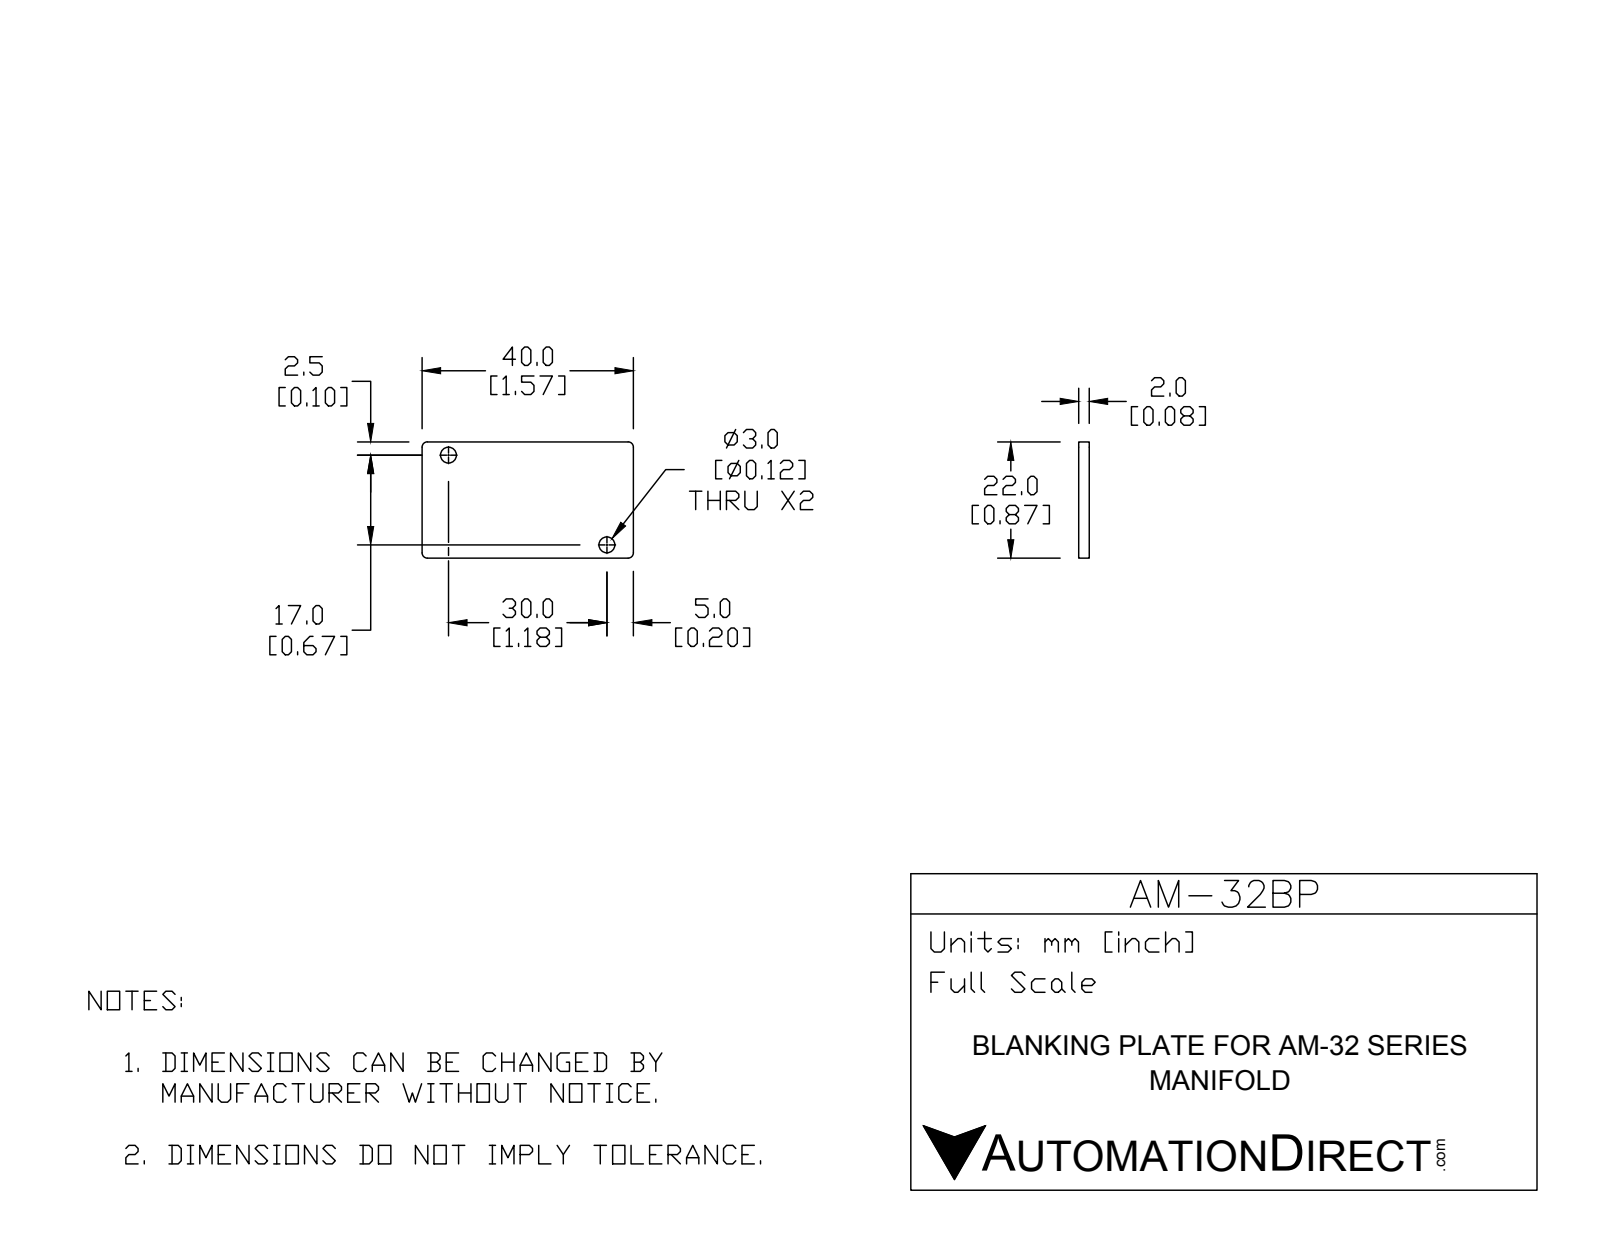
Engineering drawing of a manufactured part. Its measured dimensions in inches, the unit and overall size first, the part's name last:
Units: inches
Overall size (bounding box): 1.575 × 0.866 × 0.079
Round holes (diameter × count): ⌀0.118 ×2
Partial cylindrical surfaces — rounded edges, fillets, slot ends (radius × count): R0.039 ×4
Main face-to-face distances: 0.079, 0.866, 1.575
Hole centre spacings: 1.357
Volume: 0.106 in³ · Surface area: 3.119 in²
Bodies: 1 solid, 14 faces (6 planar, 8 cylindrical, 0 other)
Part name (STEP PRODUCT): AM-32BP
STEP written by: SolidWorks 2016 (AUTOMOTIVE_DESIGN)
